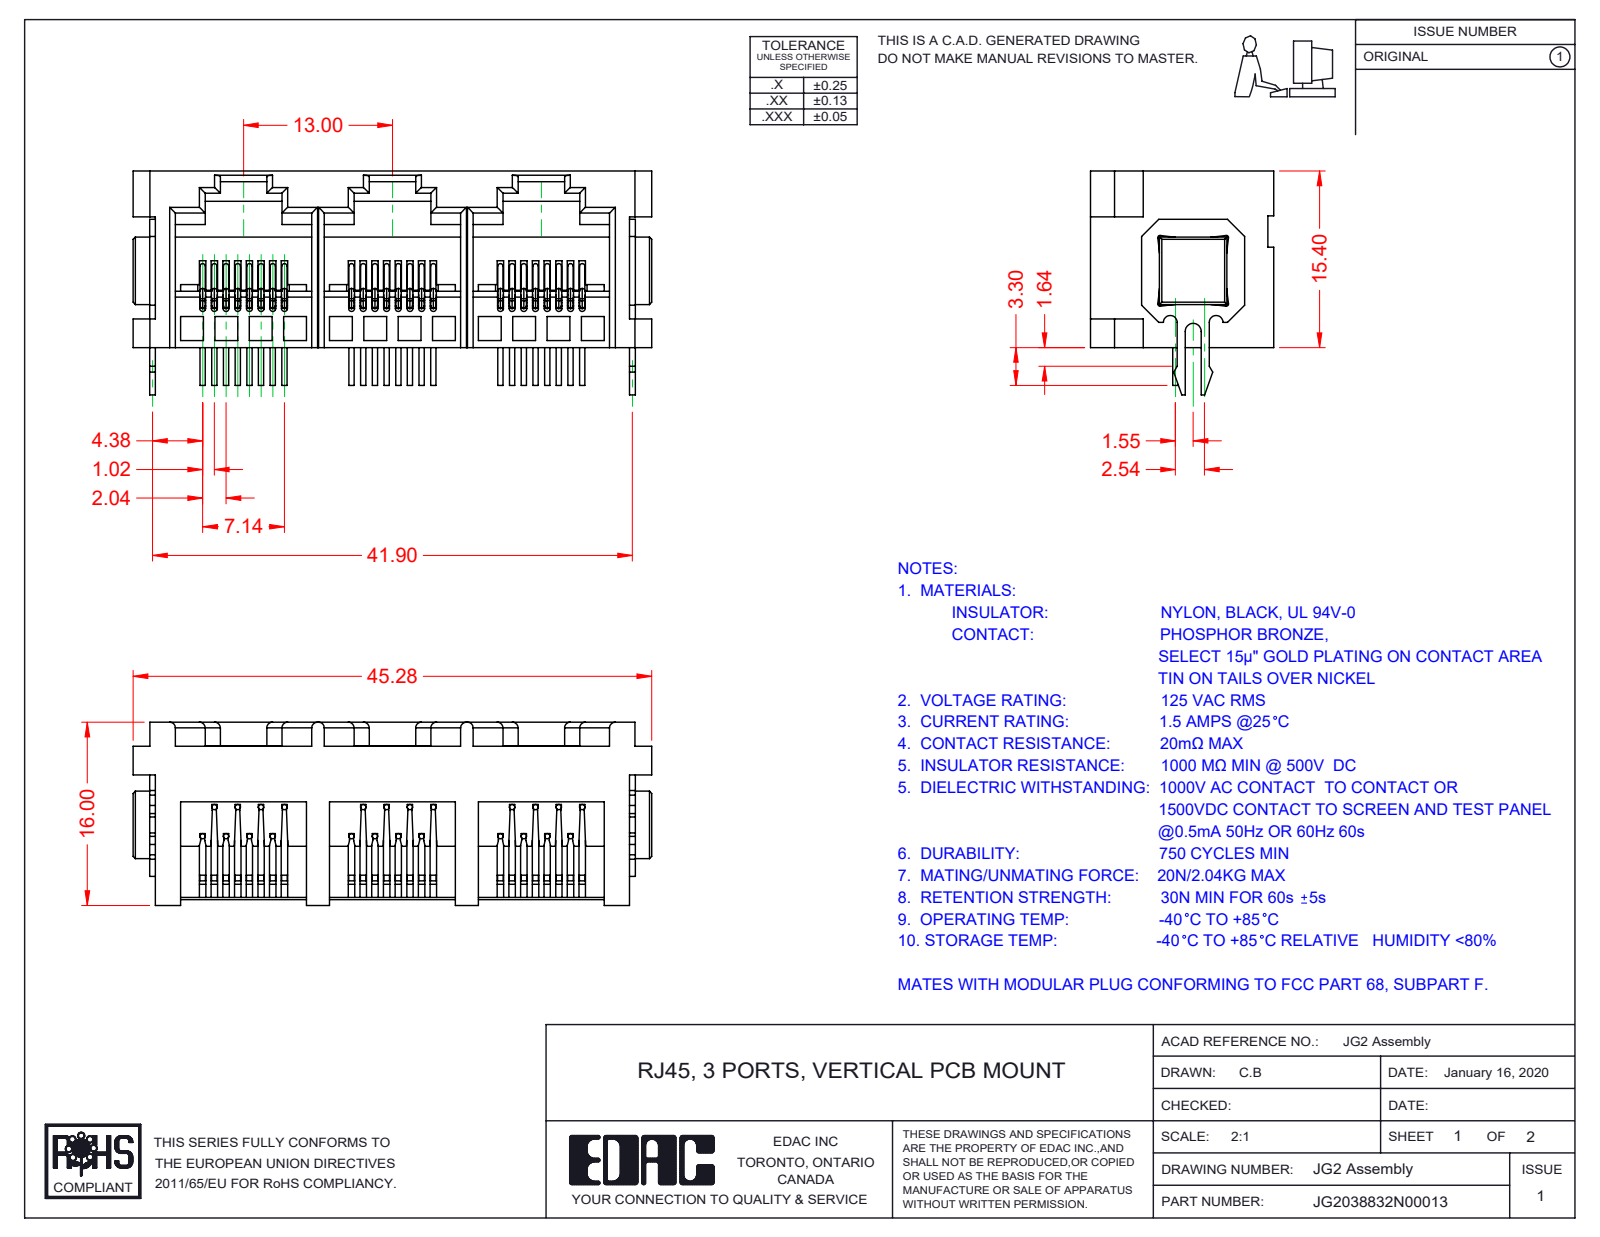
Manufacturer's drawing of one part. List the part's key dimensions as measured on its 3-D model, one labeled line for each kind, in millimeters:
Part name (STEP PRODUCT): RJG2038832N00013; G2 Boardlock2; G2 Insulator; G2 Boardlock1 (+2 more)
STEP written by: SolidWorks 2016 (CONFIG_CONTROL_DESIGN)
Units: millimetres
Bodies: 30 solids, 1835 faces (1210 planar, 457 cylindrical, 168 other)
Overall size (bounding box): 45.28 × 19.54 × 16
Volume: 4 876 mm³ · Surface area: 9 571 mm²
Round bosses / shafts (diameter × count): ⌀0.46 ×96
Partial cylindrical surfaces — rounded edges, fillets, slot ends (radius × count): R0.5 ×69, R0.2 ×4, R20.35 ×4, R0.3 ×3, R0.6 ×2, R0.21 ×1, R0.45 ×1, R0.7 ×1
Main face-to-face distances: 13, 12, 0.5, 3.4, 2.2, 11.08, 0.92, 26, 11, 2
